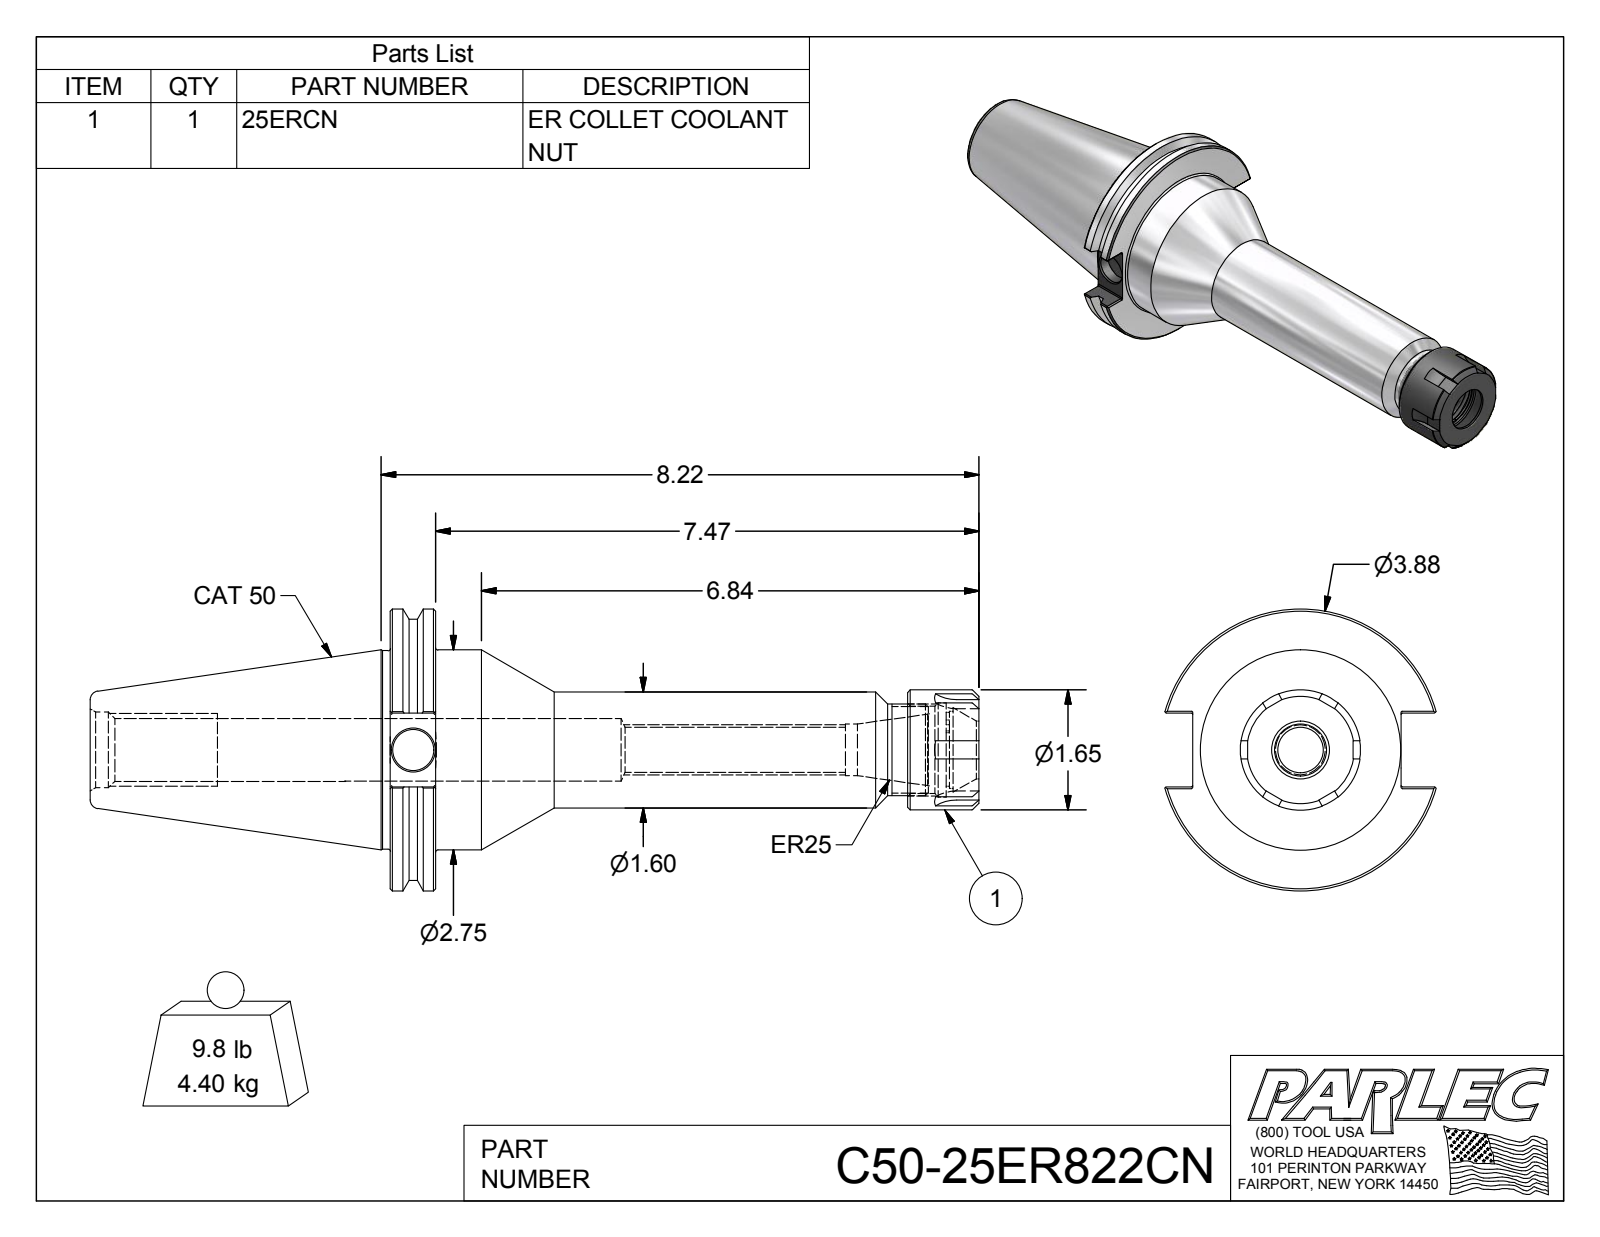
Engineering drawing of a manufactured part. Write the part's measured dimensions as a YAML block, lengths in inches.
part_name: "C50-25ER822CN; C50-25ER8-1; 25ERCN"
step_written_by: "Autodesk Inventor 2012 (AUTOMOTIVE_DESIGN)"
units: inches
bodies: {solids: 2, faces: 139, planar: 55, cylindrical: 44, other: 40}
overall_size: [12.22, 3.875, 3.729]
volume: 34.69
surface_area: 129.6
round_holes:
  - {diameter: 0.563, count: 1}
  - {diameter: 0.62, count: 1}
  - {diameter: 0.71, count: 1}
  - {diameter: 0.794, count: 1}
  - {diameter: 0.864, count: 1}
  - {diameter: 0.865, count: 1}
  - {diameter: 1.038, count: 1}
  - {diameter: 1.057, count: 1}
  - {diameter: 1.201, count: 1}
  - {diameter: 1.294, count: 1}
round_bosses_or_shafts:
  - {diameter: 3.875, count: 1}
  - {diameter: 3.594, count: 1}
  - {diameter: 2.75, count: 1}
  - {diameter: 2.73, count: 1}
  - {diameter: 1.654, count: 1}
  - {diameter: 1.595, count: 1}
  - {diameter: 1.26, count: 1}
partial_cylinders:
  - {radius: 0.02, count: 12}
  - {radius: 0.5, count: 6}
  - {radius: 0.472, count: 1}
  - {radius: 0.515, count: 1}
face_to_face_distances: [0.625, 8.095, 7.47, 7.111, 6.486, 0.984, 7.642, 7.017, 0.531, 0.453]
